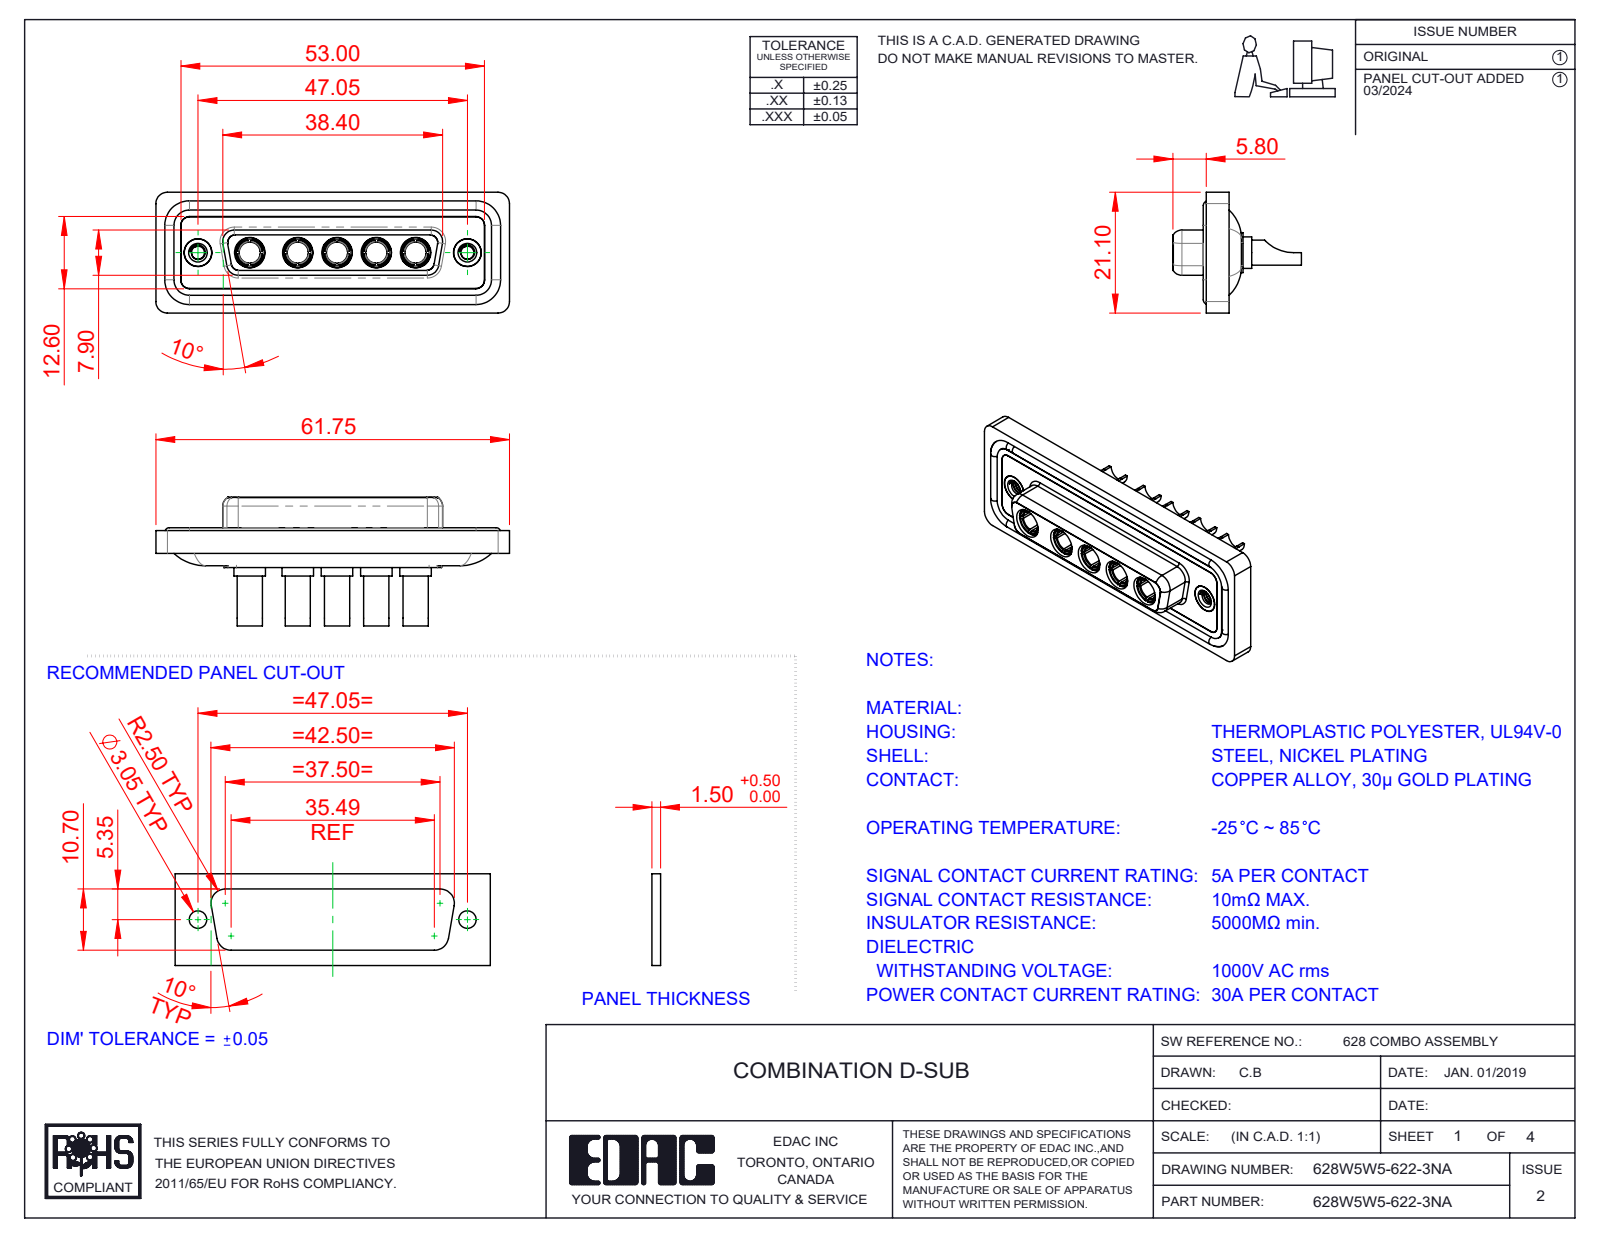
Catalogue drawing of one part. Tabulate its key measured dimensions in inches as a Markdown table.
| quantity | value |
| --- | --- |
| part name | 628Combo Shell Rear_25 Contacts; 628W5W5-622-3NA; 628Combo Waterproof Housing_25 Contacts; Power Socket_30A SC (+3 more) |
| STEP written by | SolidWorks 2023 (CONFIG_CONTROL_DESIGN) |
| units | inches |
| bodies | 17 solids, 784 faces (265 planar, 320 cylindrical, 199 other) |
| overall size | 2.431 × 0.884 × 0.831 |
| volume | 0.506 in³ |
| surface area | 21.62 in² |
| round holes (diameter × count) | 0.191 × 7, 0.138 × 5, 0.146 × 5, 0.209 × 5, 0.089 × 2, 0.157 × 2, 0.159 × 2, 0.197 × 2 |
| round bosses / shafts (diameter × count) | 0.217 × 5, 0.205 × 5, 0.195 × 5, 0.187 × 5, 0.173 × 5, 0.148 × 5, 0.063 × 4, 0.195 × 2 |
| partial cylindrical surfaces (radius × count) | 0.059 × 22, 0.079 × 18, 0.053 × 8, 0.063 × 8, 0.083 × 5, 0.01 × 4, 0.02 × 4, 0.024 × 4 |
| main face-to-face distances | 0.016, 0.071, 0.293, 0.222, 0.02, 0.278, 0.26, 0.063, 0.043, 0.114 |
| hole center spacings | 0.27, 0.356, 0.54, 1.496, 0.33, 0.6, 0.626, 0.686 |
